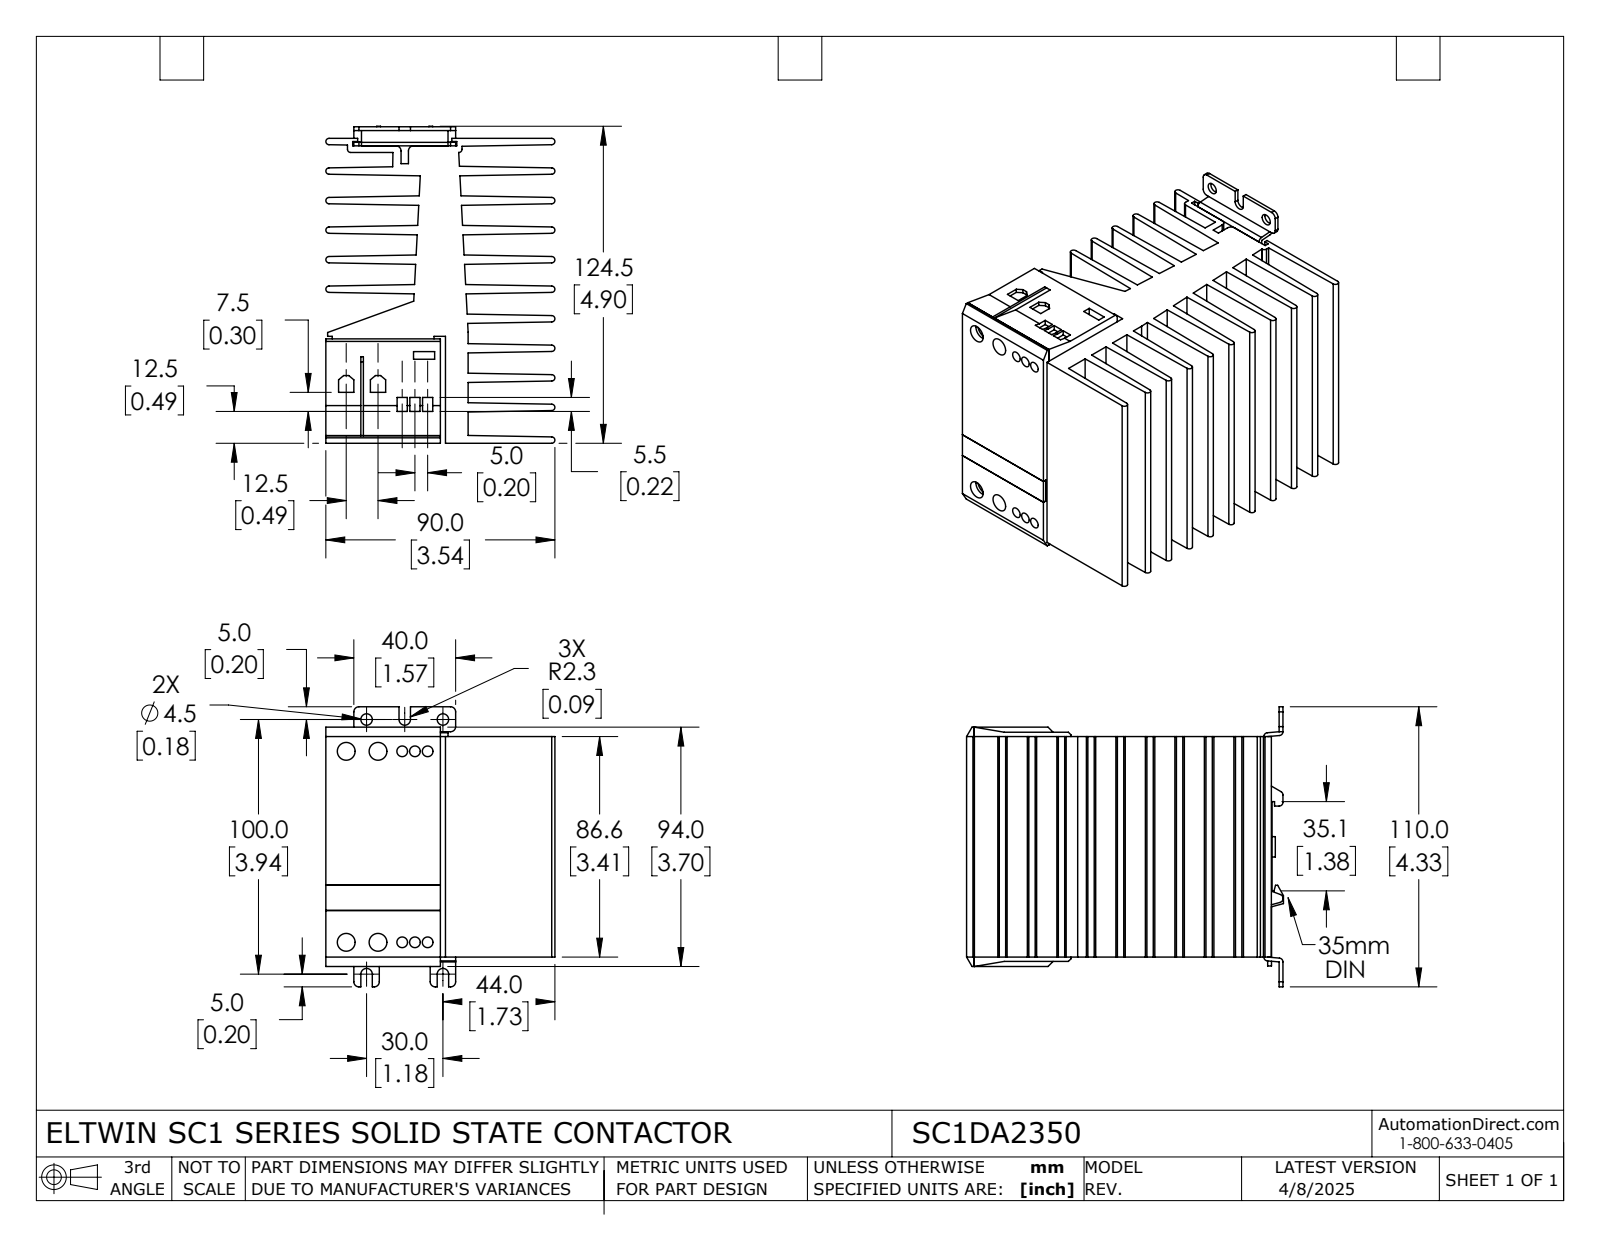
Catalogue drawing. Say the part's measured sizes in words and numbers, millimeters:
The part is named "SC1DA2350". Its 3-D file was written by "SolidWorks 2021 (AUTOMOTIVE_DESIGN)". It is 7 solids with 404 faces: 294 planar, 110 cylindrical and 0 other. Overall it measures 124.5 by 110 by 90 millimeters. Its volume is 511 300 cubic millimeters and its surface area 179 000 square millimeters. Round holes: 6 of diameter 4.2, 6 of diameter 4.4, 4 of diameter 7, 2 of diameter 4.5, 2 of diameter 8. Round bosses or shafts: 3 of diameter 8. Partial cylindrical surfaces (rounded edges, fillets, slot ends): 19 of radius 1.2, 18 of radius 2, 10 of radius 1.5, 4 of radius 1.3, 3 of radius 2.3. The main face-to-face distances are 11.6, 23.2, 34.8, 4, 7.6, 4, 46.4, 42.4, 46.4, 54. The hole center spacings are 75, 5, 75.2, 9.5, 10, 12.5, 14.5, 19.5.
